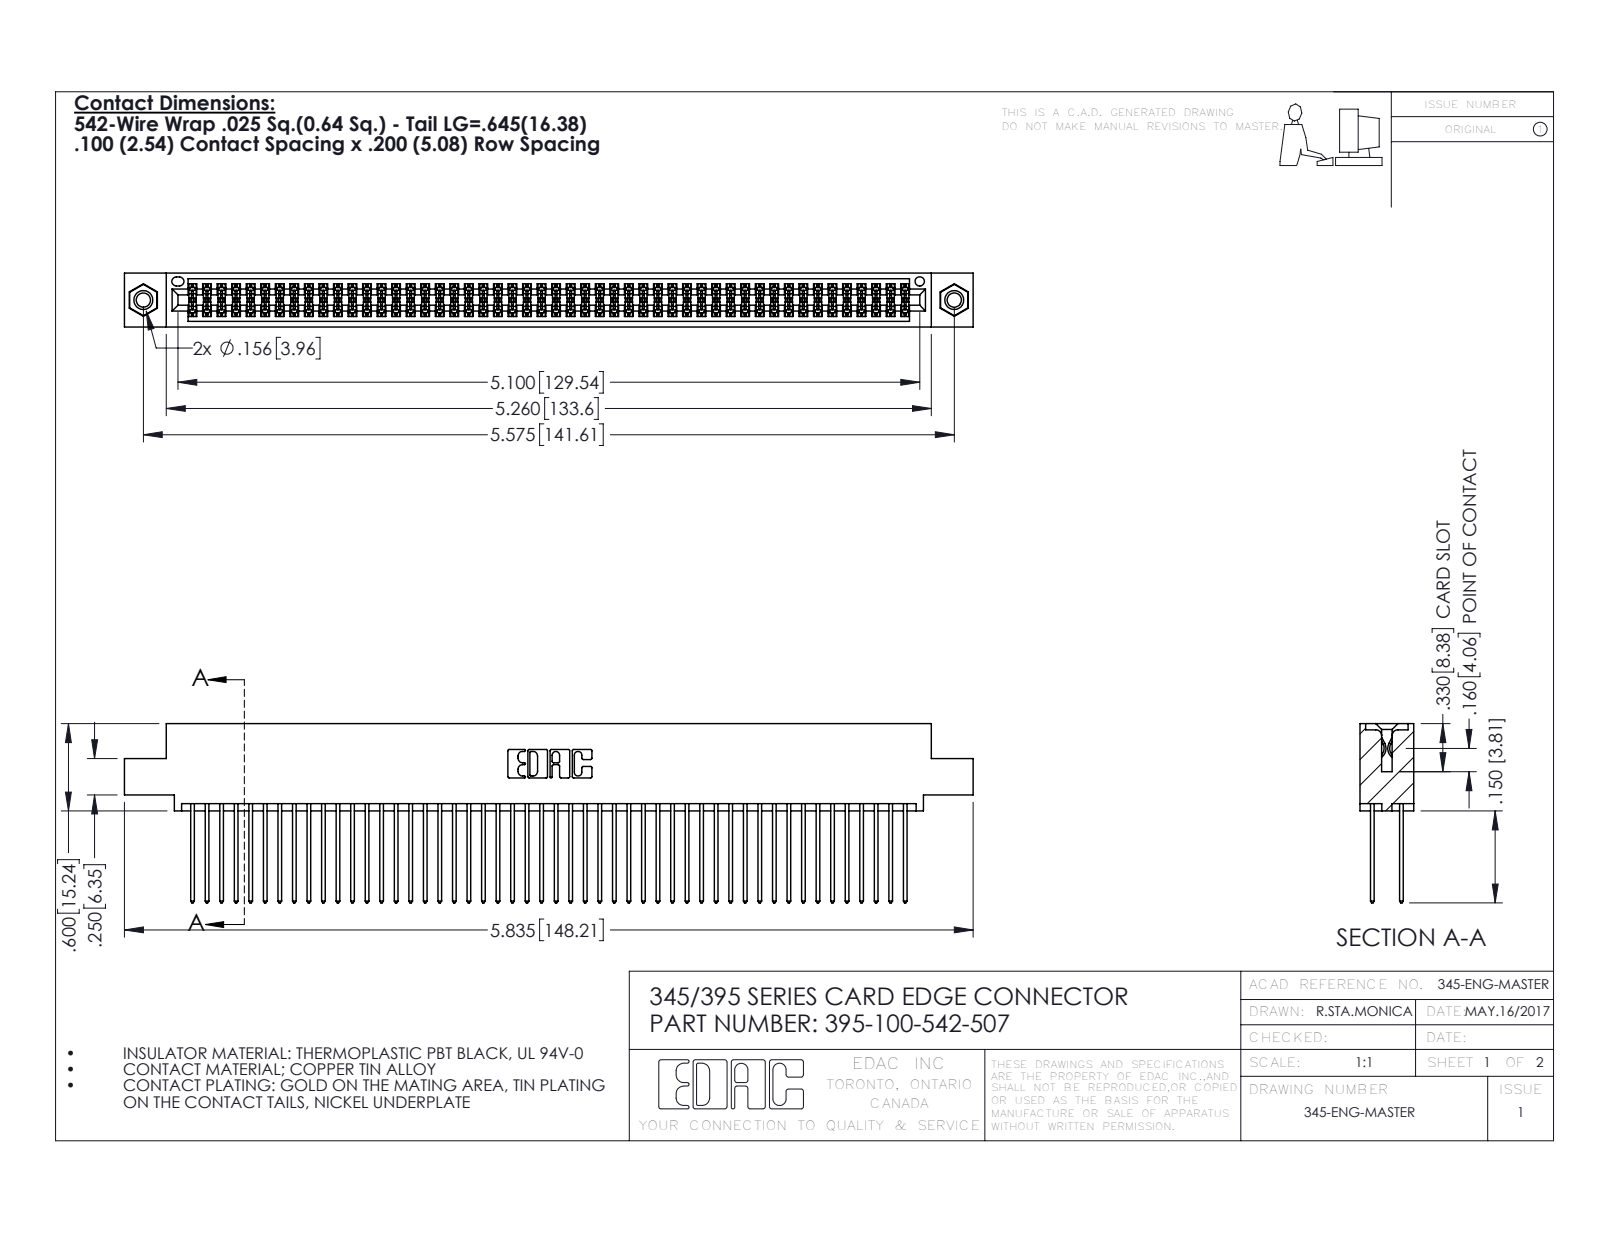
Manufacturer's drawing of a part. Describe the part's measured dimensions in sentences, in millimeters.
The part is named "345-292-001_345-293-142; 345 Part_0.110 Offset - 0.156 Dia-TI; 395-100-542-507; 345-250-001_345-250-005-103". Its 3-D file was written by "SolidWorks 2016 (CONFIG_CONTROL_DESIGN)". It is 103 solids with 5190 faces: 3416 planar, 1758 cylindrical and 16 other. Overall it measures 148.2 by 31.3 by 9.4 millimeters. Its volume is 14 800 cubic millimeters and its surface area 24 410 square millimeters. Round holes: 2 of diameter 2.5, 2 of diameter 3.2, 2 of diameter 4, 1 of diameter 1.6. Round bosses or shafts: 2 of diameter 3.9. Partial cylindrical surfaces (rounded edges, fillets, slot ends): 150 of radius 0.2, 100 of radius 0.3, 22 of radius 0.3, 6 of radius 0.2, 6 of radius 0.8, 3 of radius 0.7, 2 of radius 0.4, 2 of radius 0.5. The main face-to-face distances are 1.8, 7.6, 5.1, 2.5, 6.9, 0.6, 5.7, 9.4, 4.4, 3.8. The hole center spacings are 6.9, 135.6, 141.6.
